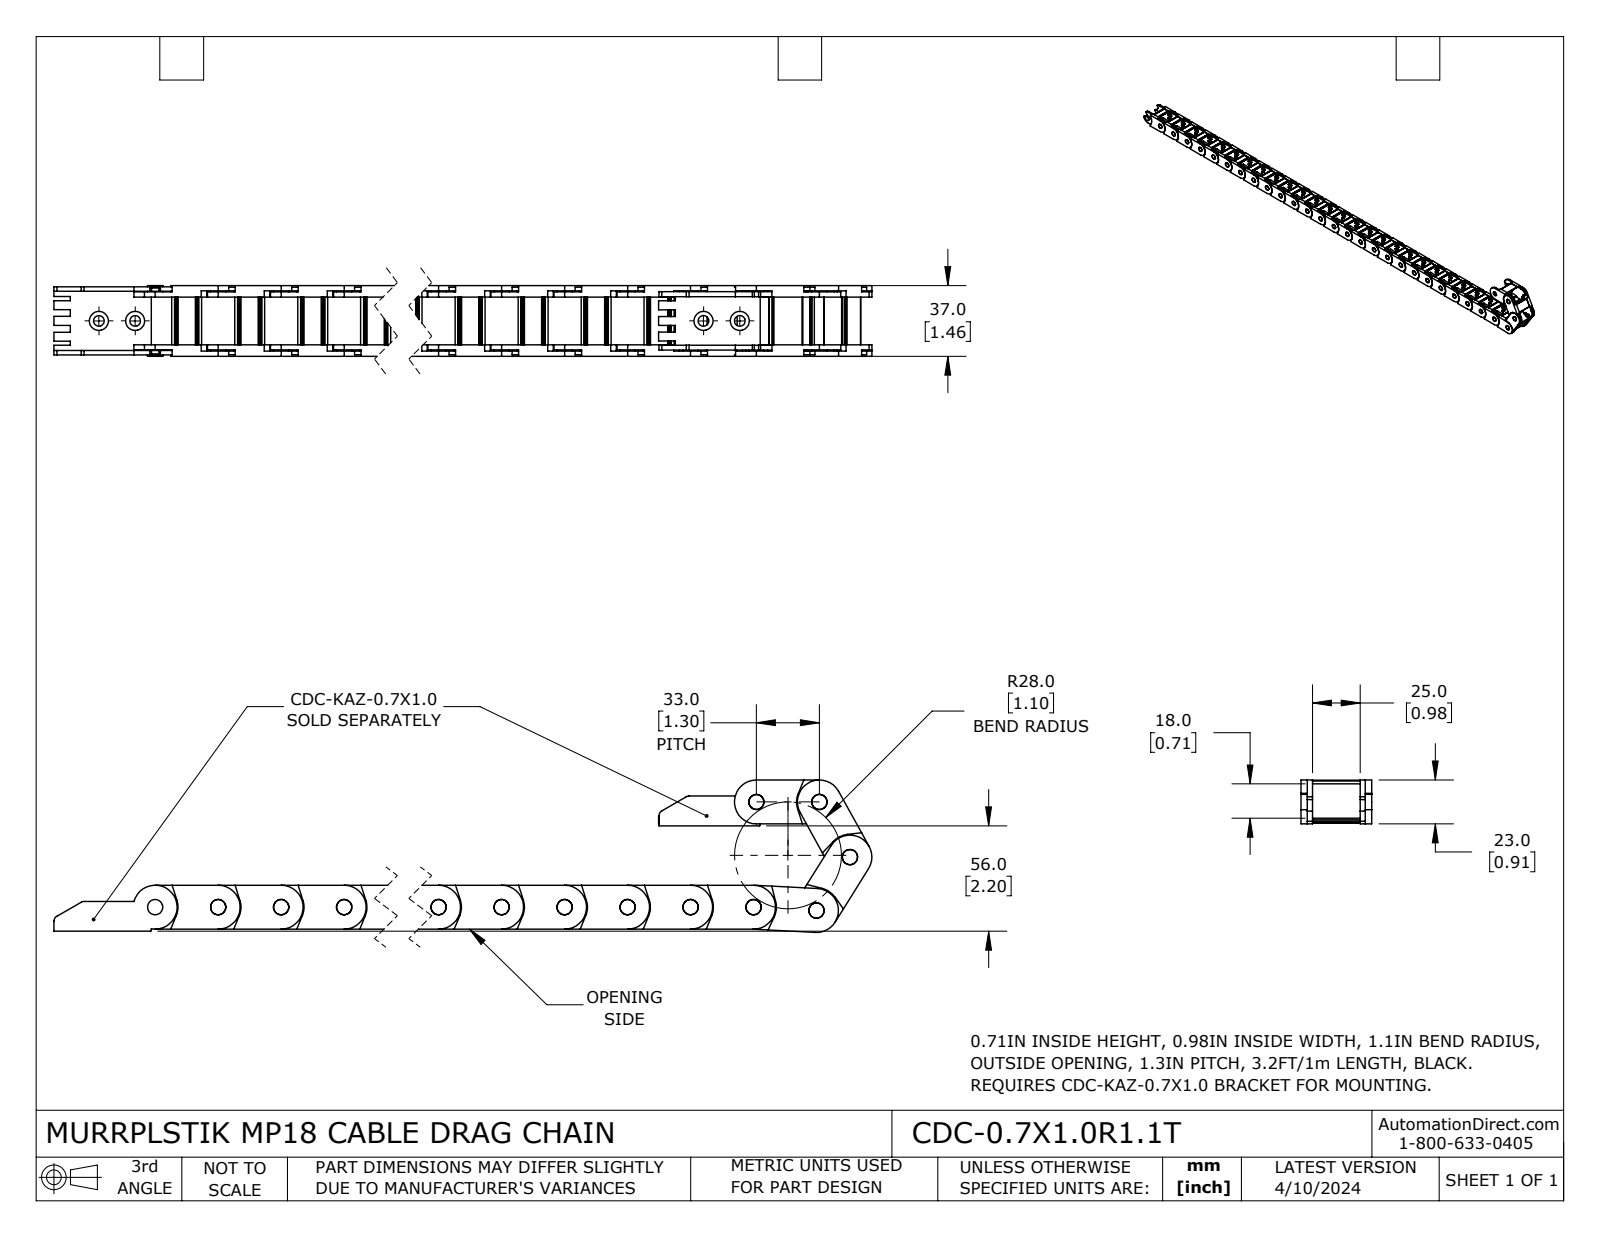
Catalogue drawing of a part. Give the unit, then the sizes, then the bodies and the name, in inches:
Units: inches
Overall size (bounding box): 36.659 × 3.143 × 1.457
Round holes (diameter × count): ⌀0.315 ×30
Round bosses / shafts (diameter × count): ⌀0.315 ×1
Partial cylindrical surfaces — rounded edges, fillets, slot ends (radius × count): R0.02 ×120, R0.059 ×120, R0.008 ×60, R0.012 ×60, R0.453 ×31, R0.47 ×31, R0.197 ×30, R0.215 ×30
Main face-to-face distances: 1.22, 0.106, 0.13, 0.236, 1.457, 1.327, 1.091, 0.984, 1.35, 0.024
Hole centre spacings: 1.299, 2.598, 3.898, 5.197, 6.496, 7.795, 9.094, 10.394
Volume: 16.69 in³ · Surface area: 339.5 in²
Bodies: 30 solids, 2490 faces (1290 planar, 1200 cylindrical, 0 other)
Part name (STEP PRODUCT): CDC-0.7X1.0R1.1T
STEP written by: SolidWorks 2023 (CONFIG_CONTROL_DESIGN)
